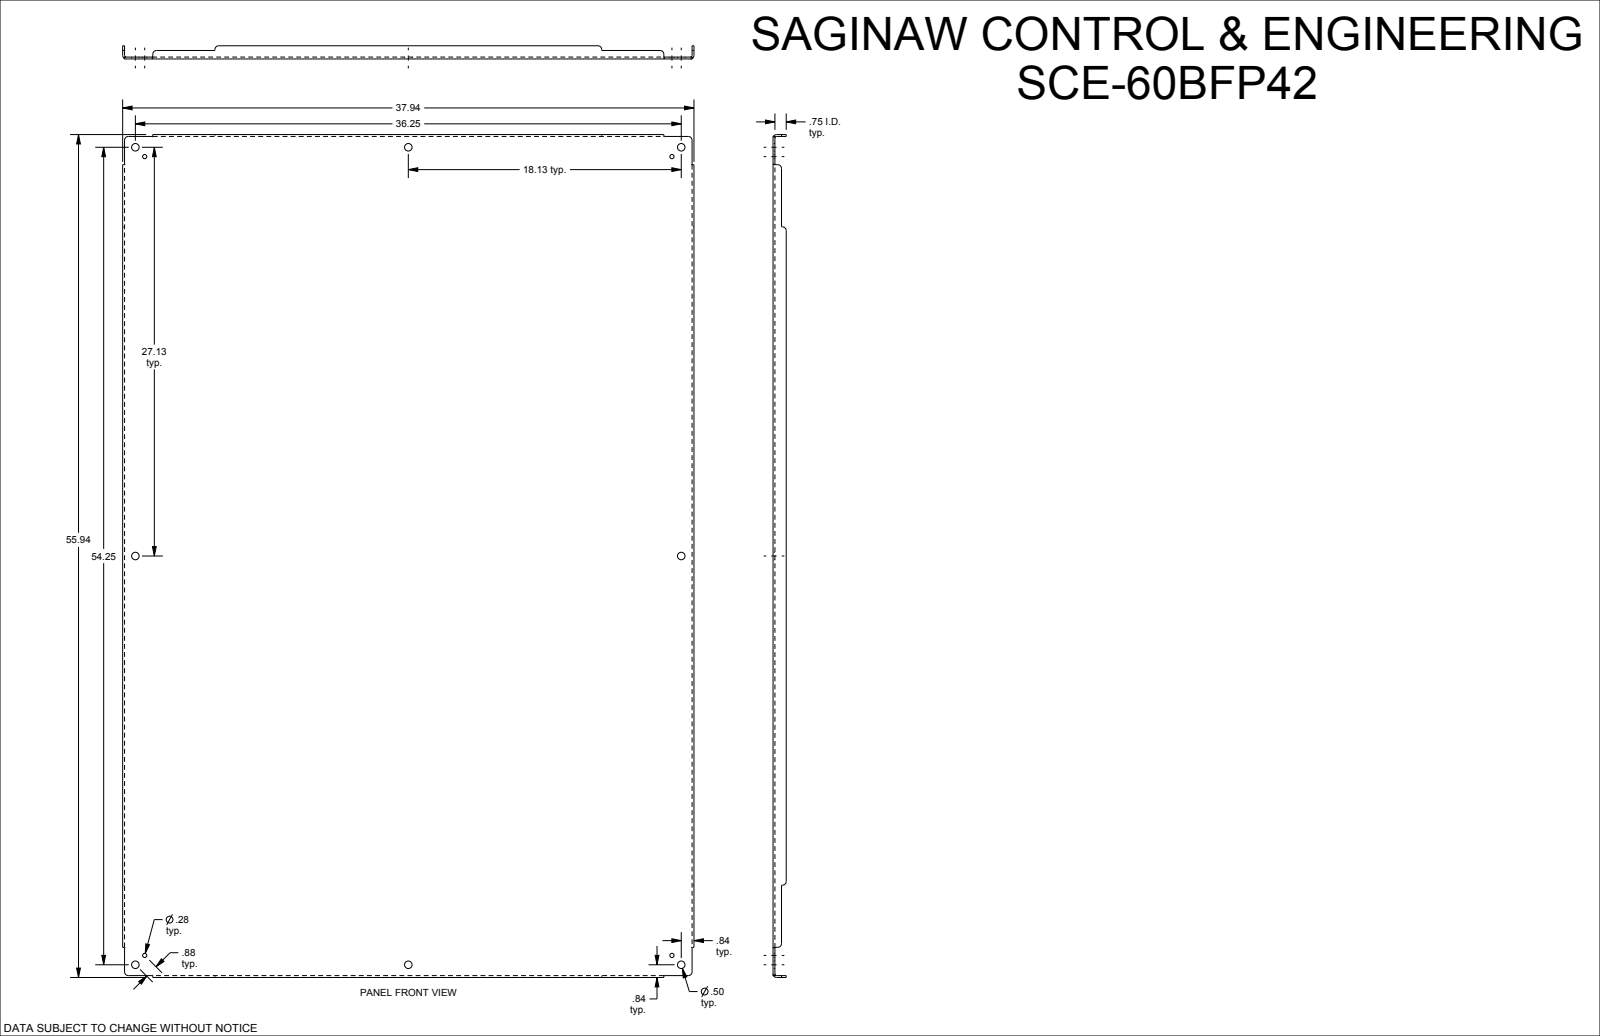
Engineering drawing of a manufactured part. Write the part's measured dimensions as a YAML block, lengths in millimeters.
part_name: "SCE-60BFP42"
step_written_by: "SolidWorks 2019 (CONFIG_CONTROL_DESIGN)"
units: millimeters
bodies: {solids: 1, faces: 110, planar: 46, cylindrical: 40, other: 24}
overall_size: [1420.8, 963.6, 22.2]
volume: 4556000
surface_area: 2886000
round_holes:
  - {diameter: 12.7, count: 8}
  - {diameter: 7.1, count: 4}
partial_cylinders:
  - {radius: 6.4, count: 12}
  - {radius: 2.8, count: 4}
  - {radius: 6, count: 4}
face_to_face_distances: [3.2, 3.2, 960.5, 1417.7, 957.2, 963.6, 1414.4, 1420.8, 19.1, 22.2]
hole_center_spacings: [22.2, 444.9, 460.4, 673.4, 689, 828.6, 905.2, 1128]
